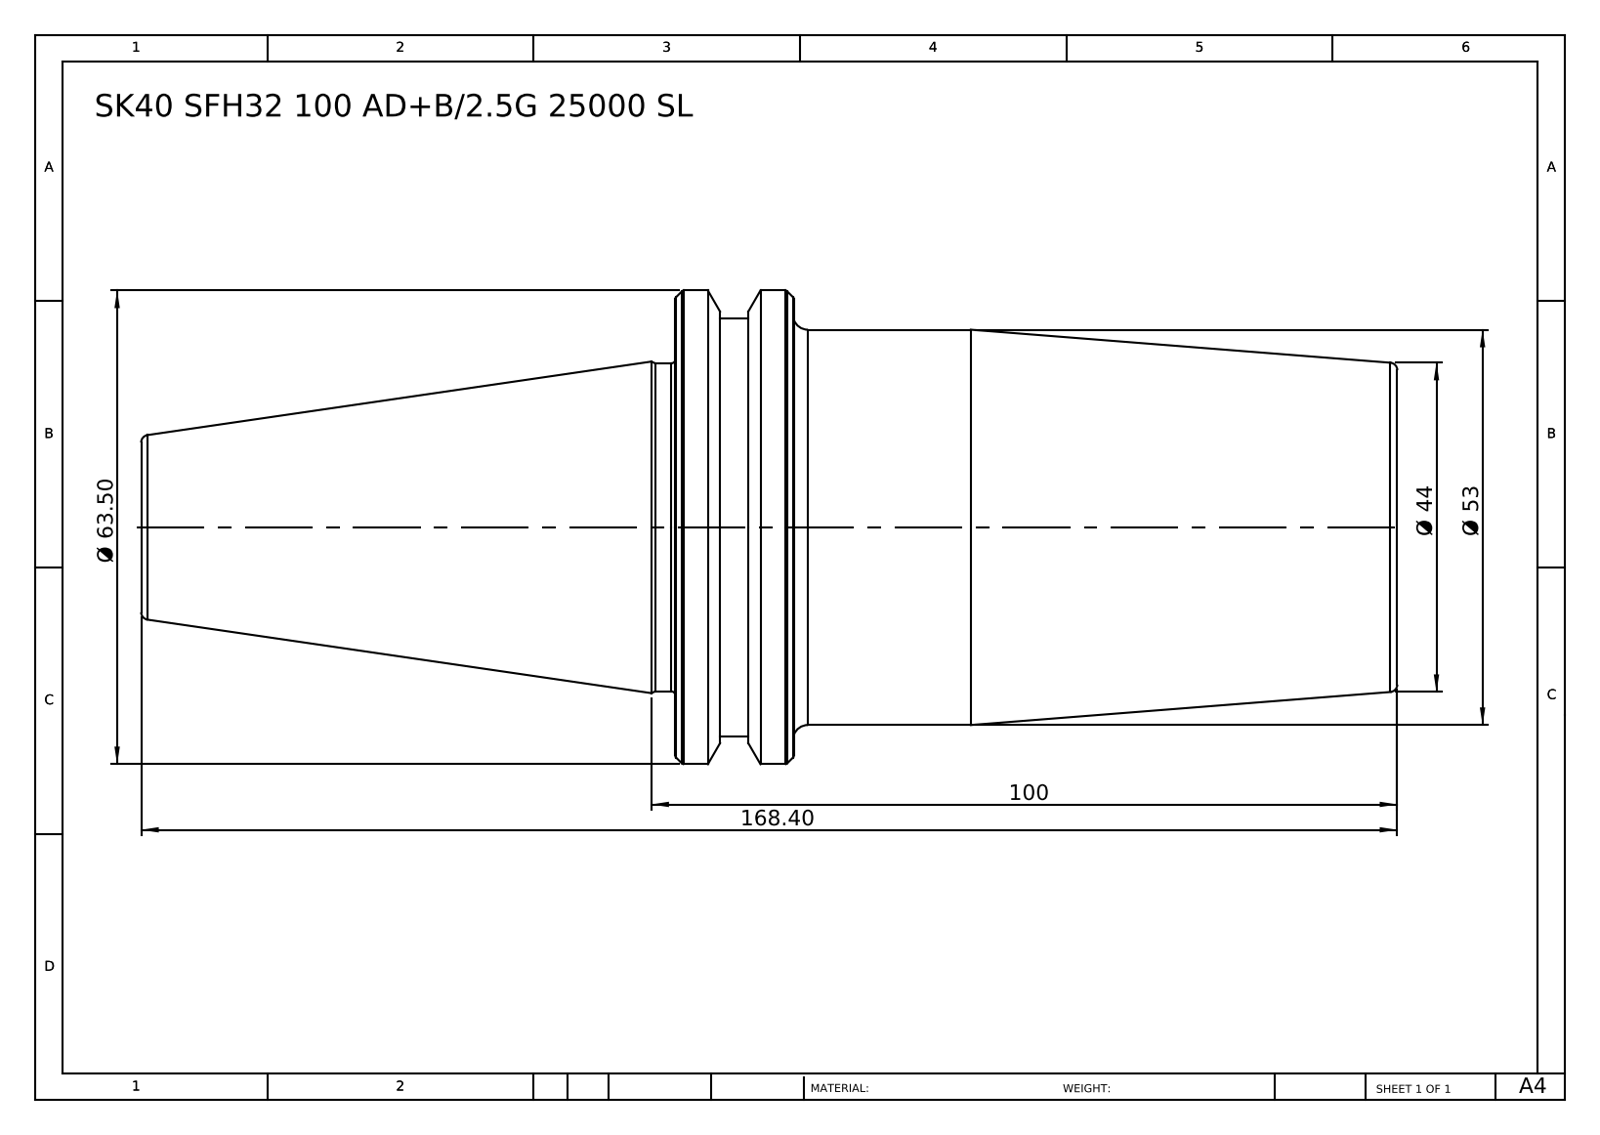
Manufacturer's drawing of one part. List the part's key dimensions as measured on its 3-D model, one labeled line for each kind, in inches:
Part name (STEP PRODUCT): SK40 SFH25 100 AD+B-2.5G 25000 SL
STEP written by: SolidWorks 2014 (CONFIG_CONTROL_DESIGN)
Units: inches
Bodies: 1 solid, 46 faces (6 planar, 10 cylindrical, 30 other)
Overall size (bounding box): 6.63 × 2.5 × 2.5
Volume: 16.81 in³ · Surface area: 44.57 in²
Round bosses / shafts (diameter × count): ⌀2.5 ×1, ⌀2.205 ×1, ⌀2.087 ×1, ⌀1.732 ×1
Main face-to-face distances: 3.811, 3.185, 0.626, 6.63, 3.445, 2.819, 3.425, 0.24, 0.386, 3.205
